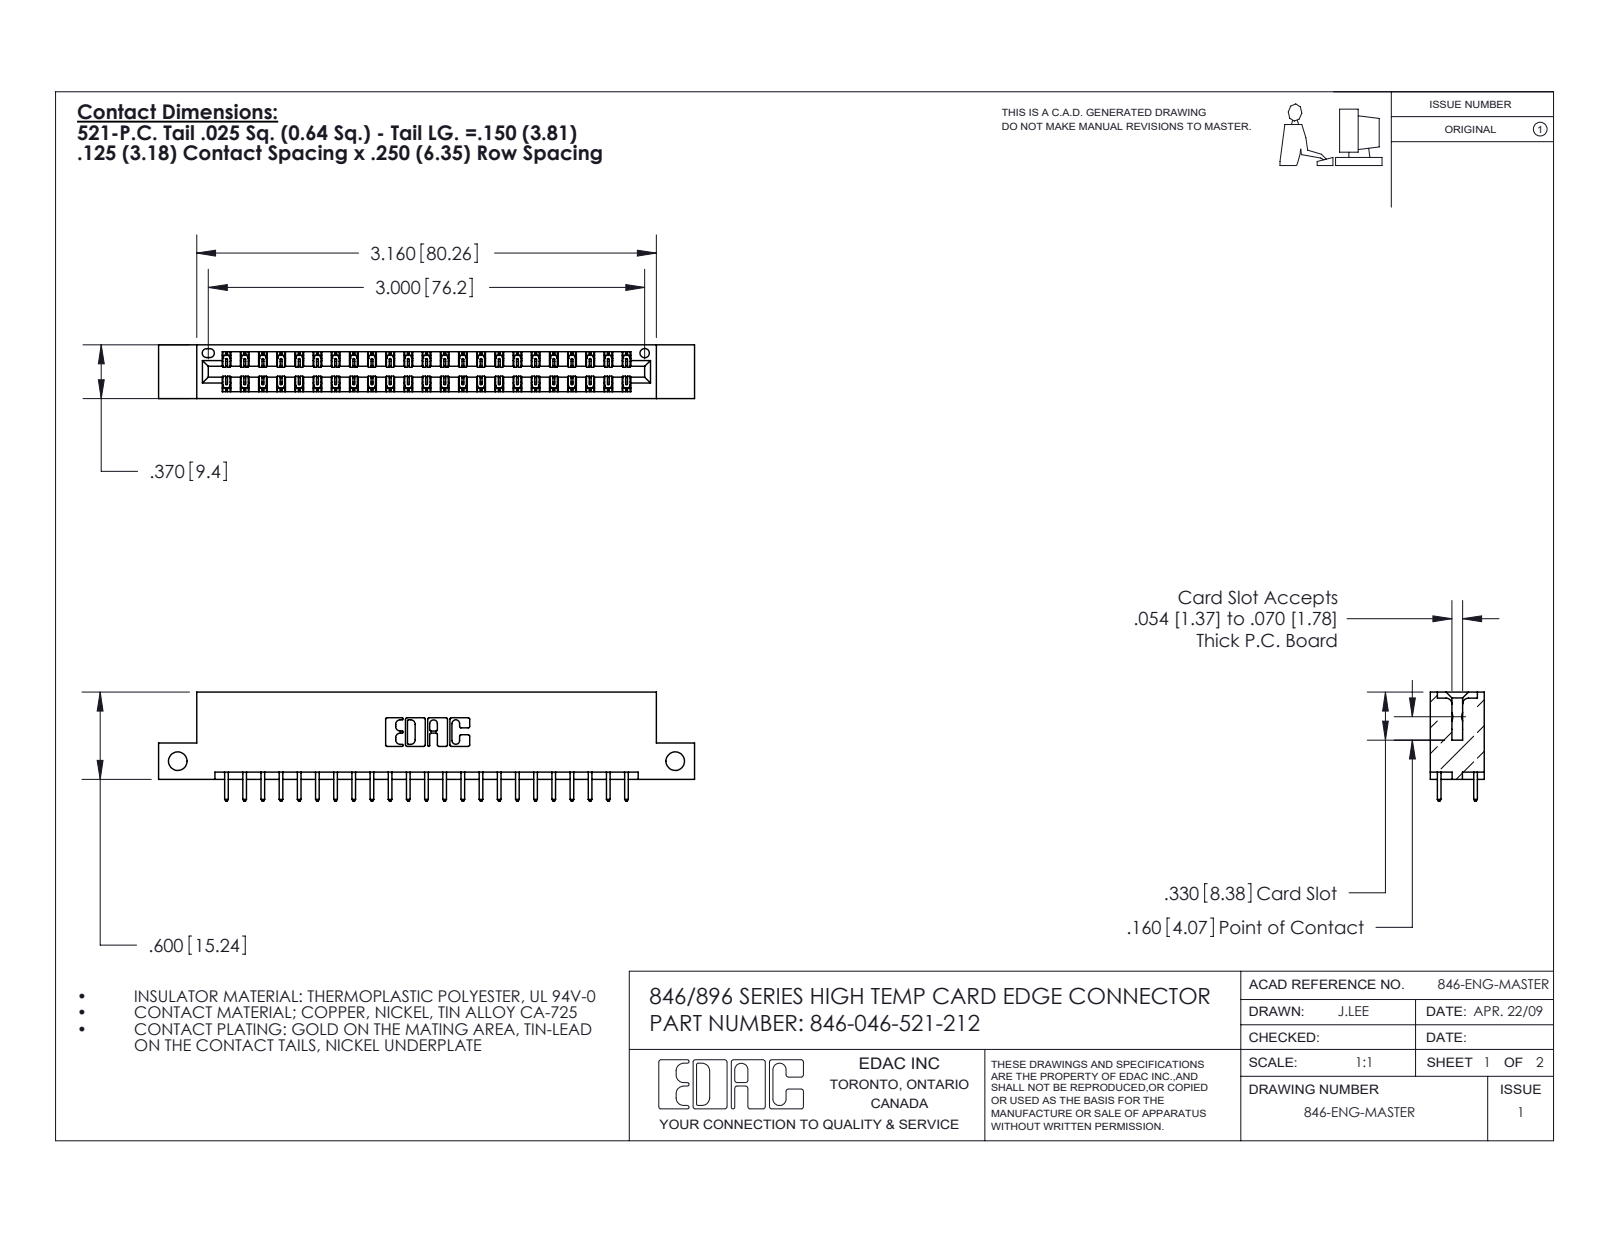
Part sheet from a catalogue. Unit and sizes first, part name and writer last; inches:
Units: inches
Overall size (bounding box): 3.685 × 0.75 × 0.37
Round holes (diameter × count): ⌀0.128 ×2, ⌀0.064 ×1
Partial cylindrical surfaces — rounded edges, fillets, slot ends (radius × count): R0.006 ×69, R0.01 ×46, R0.01 ×22, R0.007 ×6, R0.031 ×6, R0.026 ×3, R0.014 ×2, R0.022 ×2
Main face-to-face distances: 0.048, 0.322, 0.25, 0.37, 0.072, 0.298, 0.025, 0.275, 0.148, 0.222
Hole centre spacings: 3.42
Volume: 0.541 in³ · Surface area: 18.03 in²
Bodies: 47 solids, 2514 faces (1686 planar, 828 cylindrical, 0 other)
Part name (STEP PRODUCT): 346 Part_Flush Mounting Lugs - Side Mount; 346-046-521-212; 345-292-001_345-293-121
STEP written by: SolidWorks 2016 (CONFIG_CONTROL_DESIGN)
